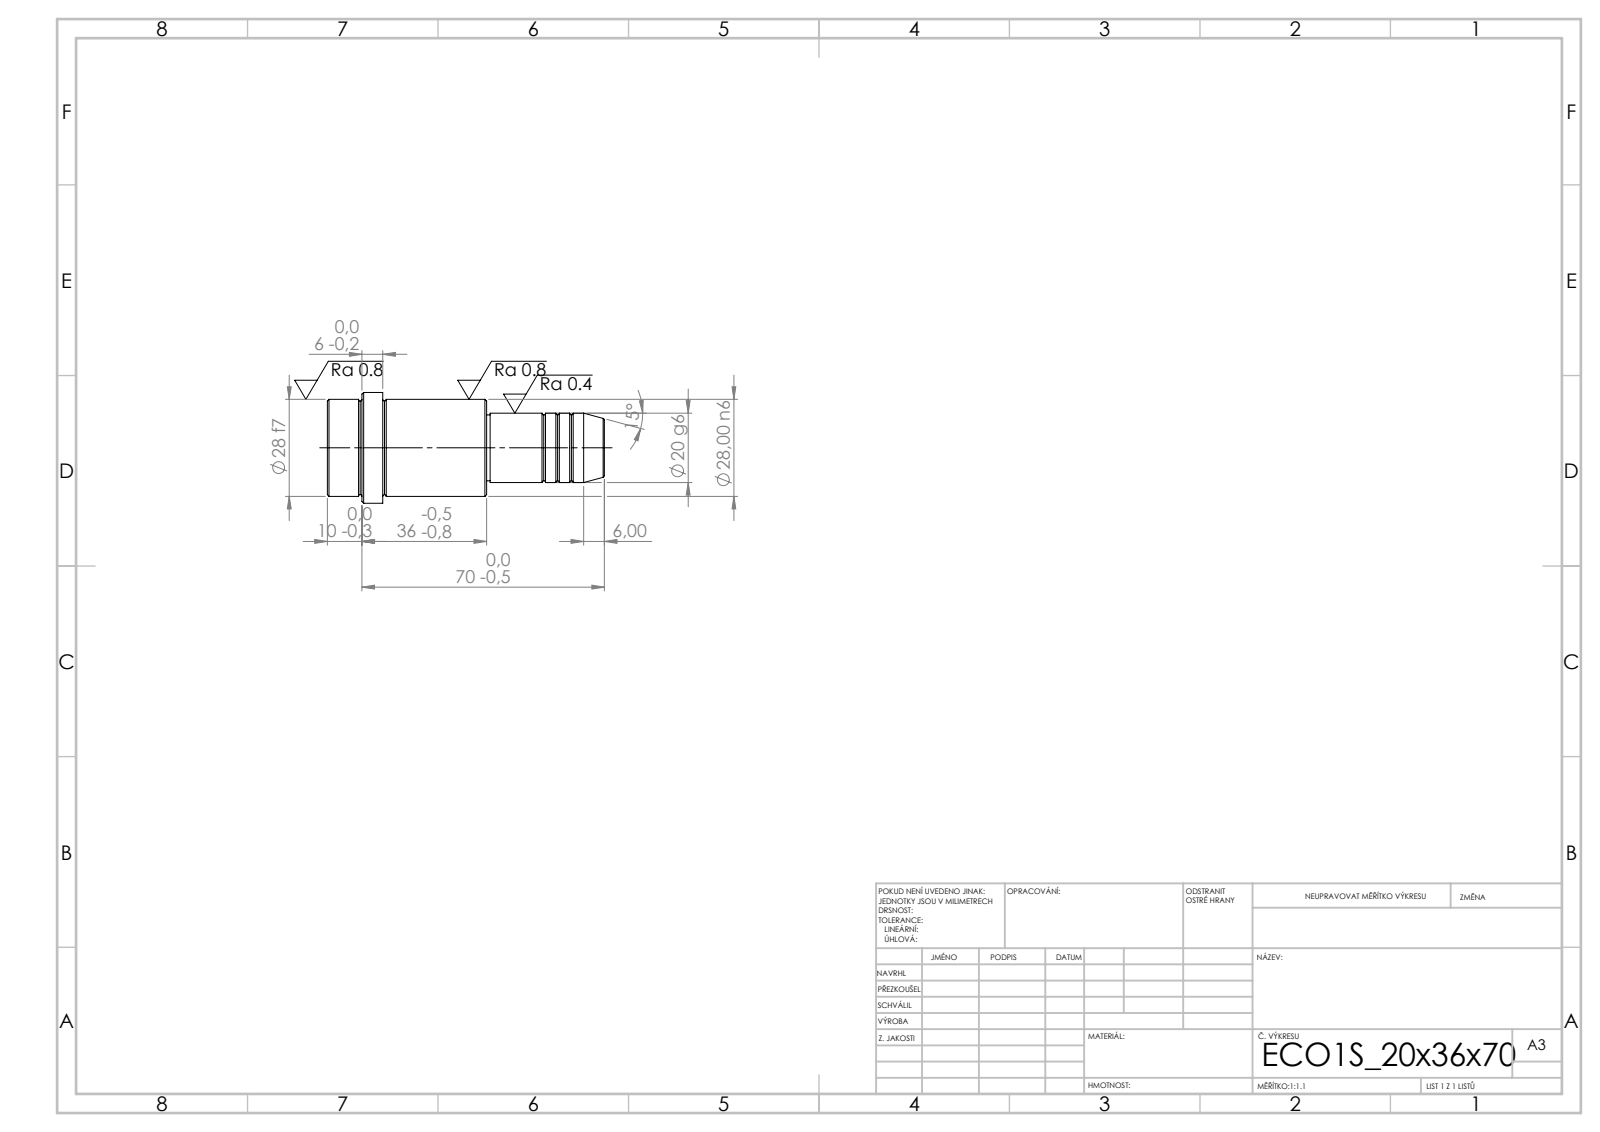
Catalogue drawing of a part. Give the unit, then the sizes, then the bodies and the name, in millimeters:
Units: millimetres
Overall size (bounding box): 80 × 32 × 32
Round bosses / shafts (diameter × count): ⌀32 ×1, ⌀28 ×1, ⌀20 ×1, ⌀19 ×1
Main face-to-face distances: 46, 34, 80, 64, 30, 16, 70, 36, 6, 10
Volume: 39 643 mm³ · Surface area: 7 918 mm²
Bodies: 1 solid, 52 faces (6 planar, 16 cylindrical, 30 other)
STEP written by: SolidWorks 2019 (CONFIG_CONTROL_DESIGN)
